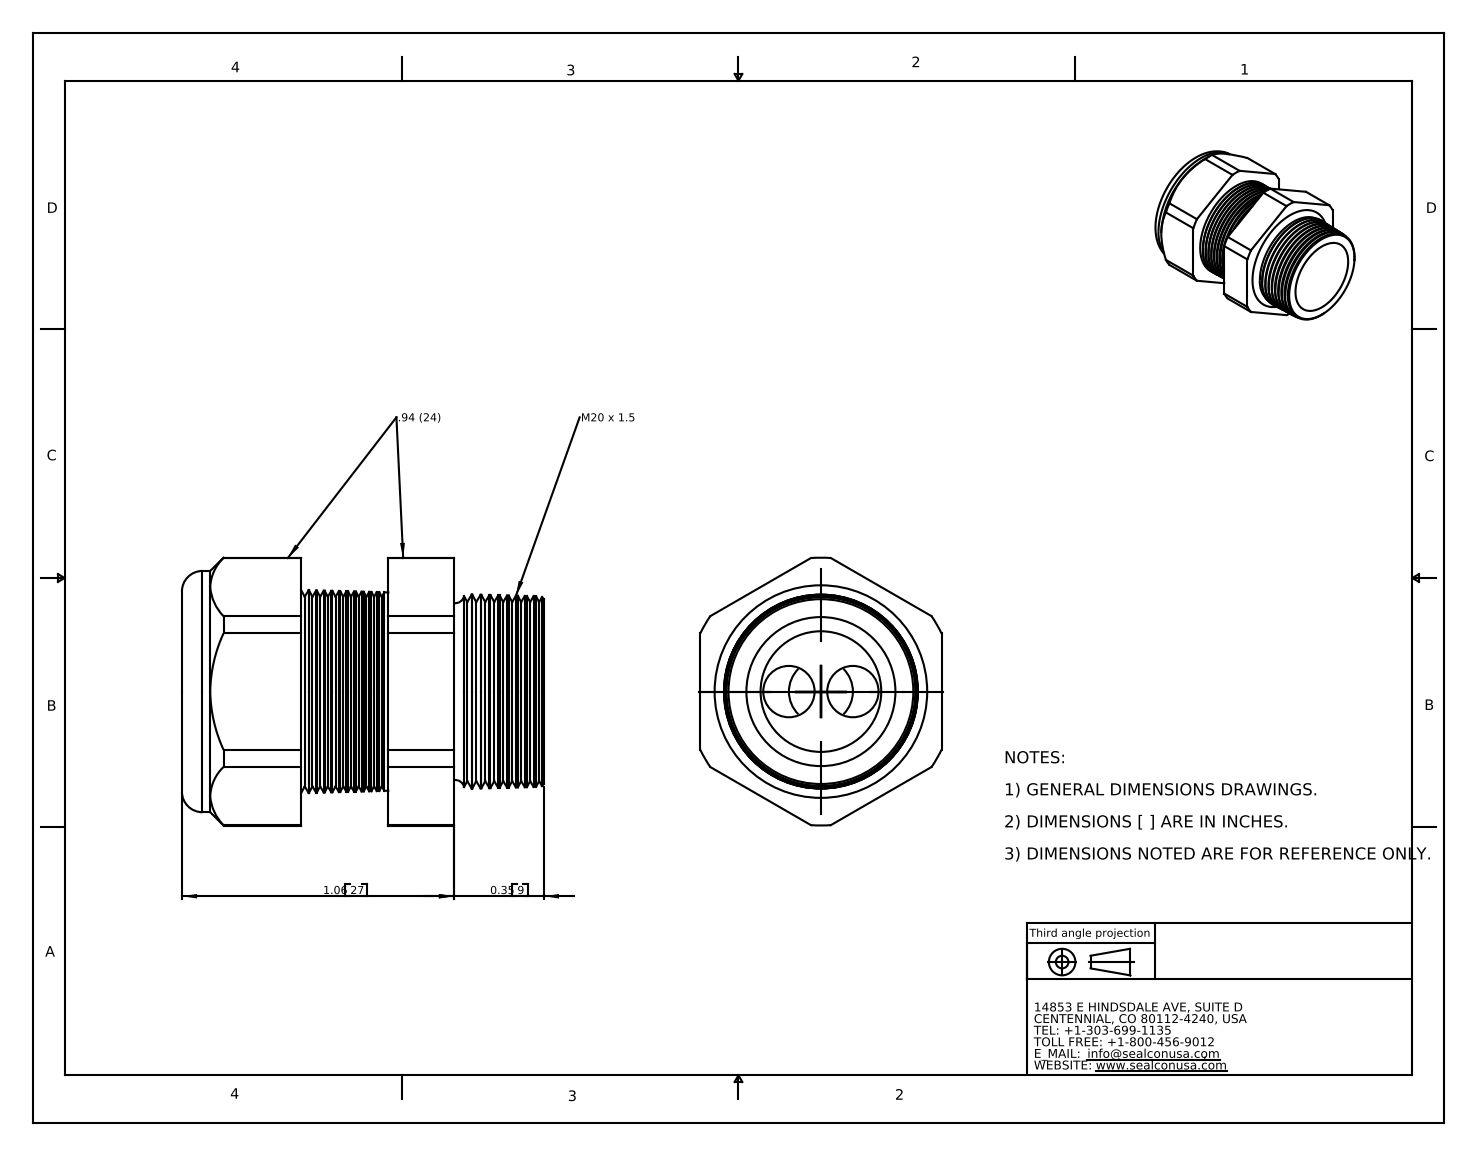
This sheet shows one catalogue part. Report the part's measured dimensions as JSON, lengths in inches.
{"part_name": "CD20M6-GY", "step_written_by": "SolidWorks 2007 (CONFIG_CONTROL_DESIGN)", "units": "inches", "bodies": {"solids": 2, "faces": 178, "planar": 20, "cylindrical": 24, "other": 134}, "overall_size": [1.41, 1.043, 0.94], "volume_in3": 0.571, "surface_area_in2": 9.904, "round_holes": [[0.2, 2], [0.45, 1], [0.47, 1]], "round_bosses_or_shafts": [[0.94, 1]], "partial_cylinders_radius": [[0.522, 1]], "face_to_face_distances": [0.94, 0.804, 0.465, 0.34, 1.06, 0.596, 0.256, 1.41, 0.946, 0.606], "hole_center_spacings": [0.124, 0.249]}
